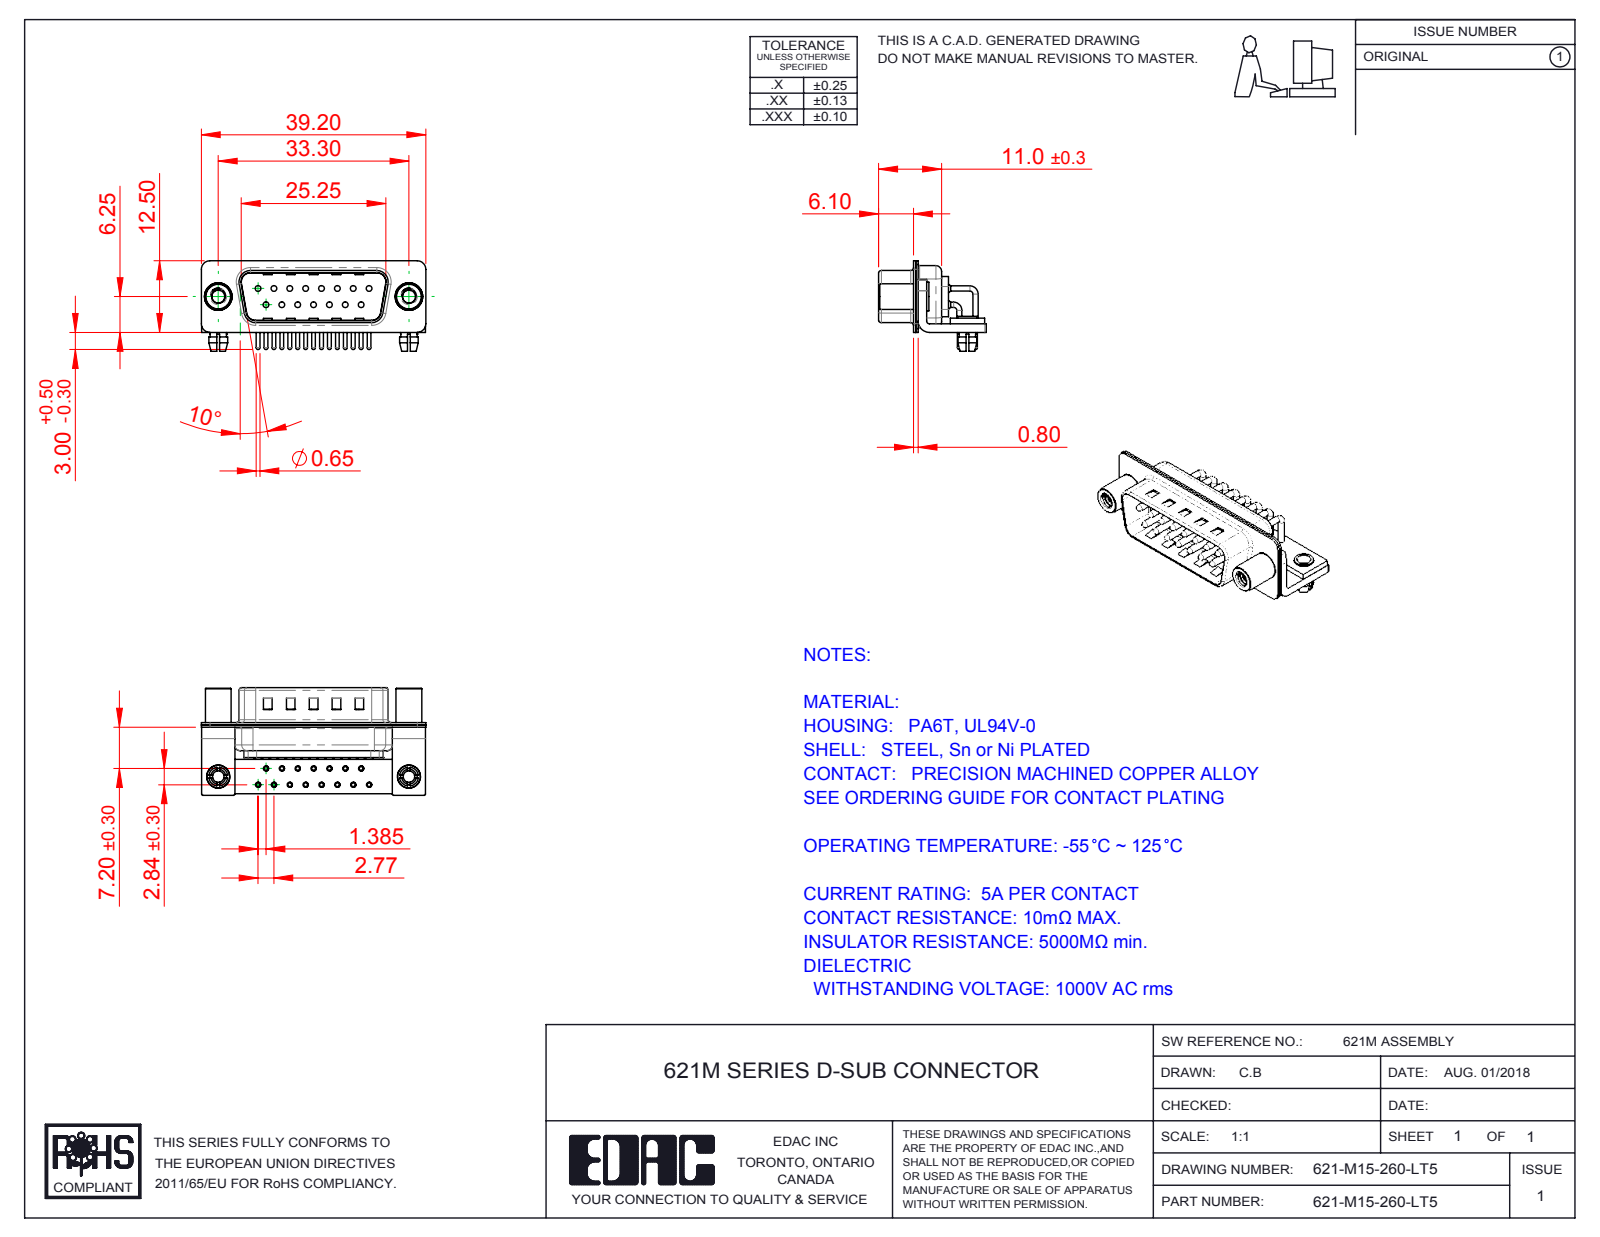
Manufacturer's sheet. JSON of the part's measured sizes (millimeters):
{"part_name": "621-M15-260-LT5; 621M Stabilizer Board_15 Contacts; 621M 4-40 Threaded Standoff; 621M Stabilizer Bracket (+6 more)", "step_written_by": "SolidWorks 2016 (CONFIG_CONTROL_DESIGN)", "units": "millimeters", "bodies": {"solids": 25, "faces": 2212, "planar": 1175, "cylindrical": 799, "other": 238}, "overall_size": [39.2, 18.8, 15.8], "volume_mm3": 2544, "surface_area_mm2": 6913, "round_holes": [[2, 17], [0.9, 15], [1, 15], [1.7, 15], [2.26, 2], [2.5, 2], [3.2, 2], [4, 2], [4.8, 2]], "round_bosses_or_shafts": [[0.9, 22], [1.5, 15], [0.65, 15], [5, 2], [4.9, 2], [4.5, 2], [4, 2], [3.4, 2]], "partial_cylinders_radius": [[0.25, 16], [1.5, 16], [1.01, 15], [2, 13], [0.5, 9], [1.6, 8], [0.6, 4], [0.65, 4]], "face_to_face_distances": [0.4, 0.85, 1.5, 0.8, 1.25, 10.4, 9.55, 1, 1.9, 8.3], "hole_center_spacings": [3.16, 2.77, 5.54, 8.31, 11.08, 5.03, 5.04, 7.48]}
